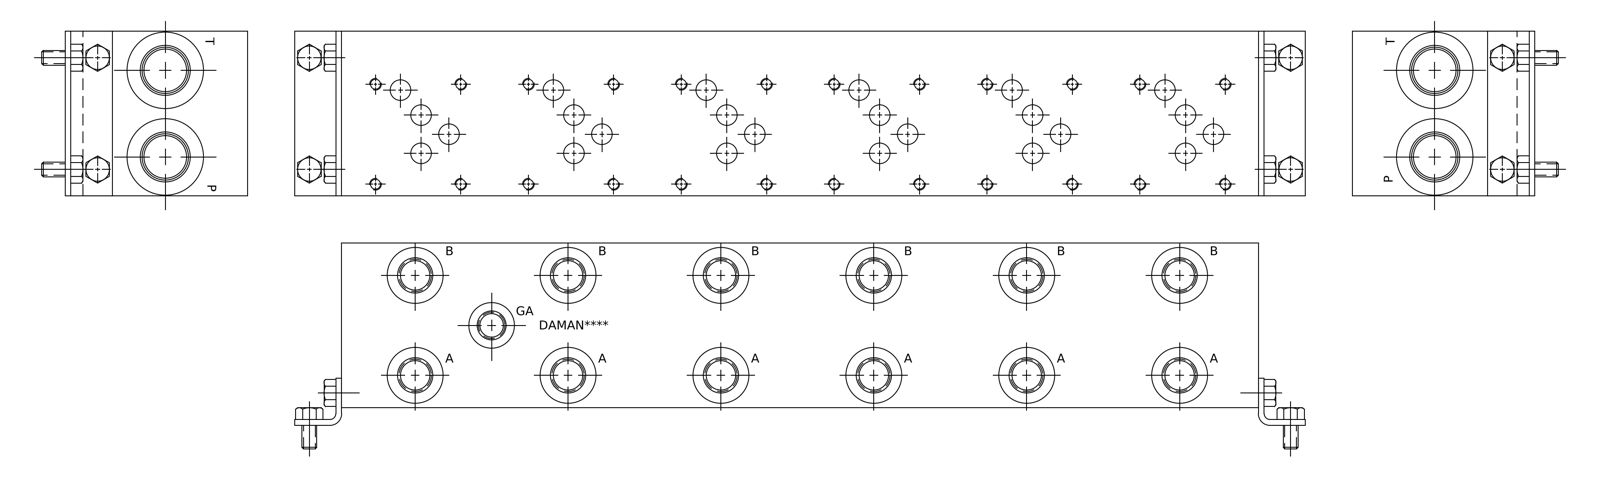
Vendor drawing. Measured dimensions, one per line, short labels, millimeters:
name: Part_AD05P063S_3D
written by: Autodesk Inventor 2019 (AUTOMOTIVE_DESIGN)
unit: mm
bodies: 1 solid, 999 faces (485 planar, 165 cylindrical, 349 other)
size: 495.3 × 88.9 × 88.9
volume: 3 727 000 mm³; area: 235 403 mm²
holes: 24× ⌀5.11, 24× ⌀6.35, 24× ⌀11.13, 12× ⌀15.88, 12× ⌀17.5, 12× ⌀19.05, 12× ⌀19.25, 12× ⌀30.63, 2× ⌀6.53, 2× ⌀7.92, 2× ⌀23.01, 2× ⌀24.92
face distances: 88.9, 0.79, 88.11, 495.3, 494.51, 493.72, 19.05, 15.06, 14.27, 73.84
hole spacings: 82.55, 165.1, 247.65, 98.63, 253.46, 173.7, 46.05, 53.98
